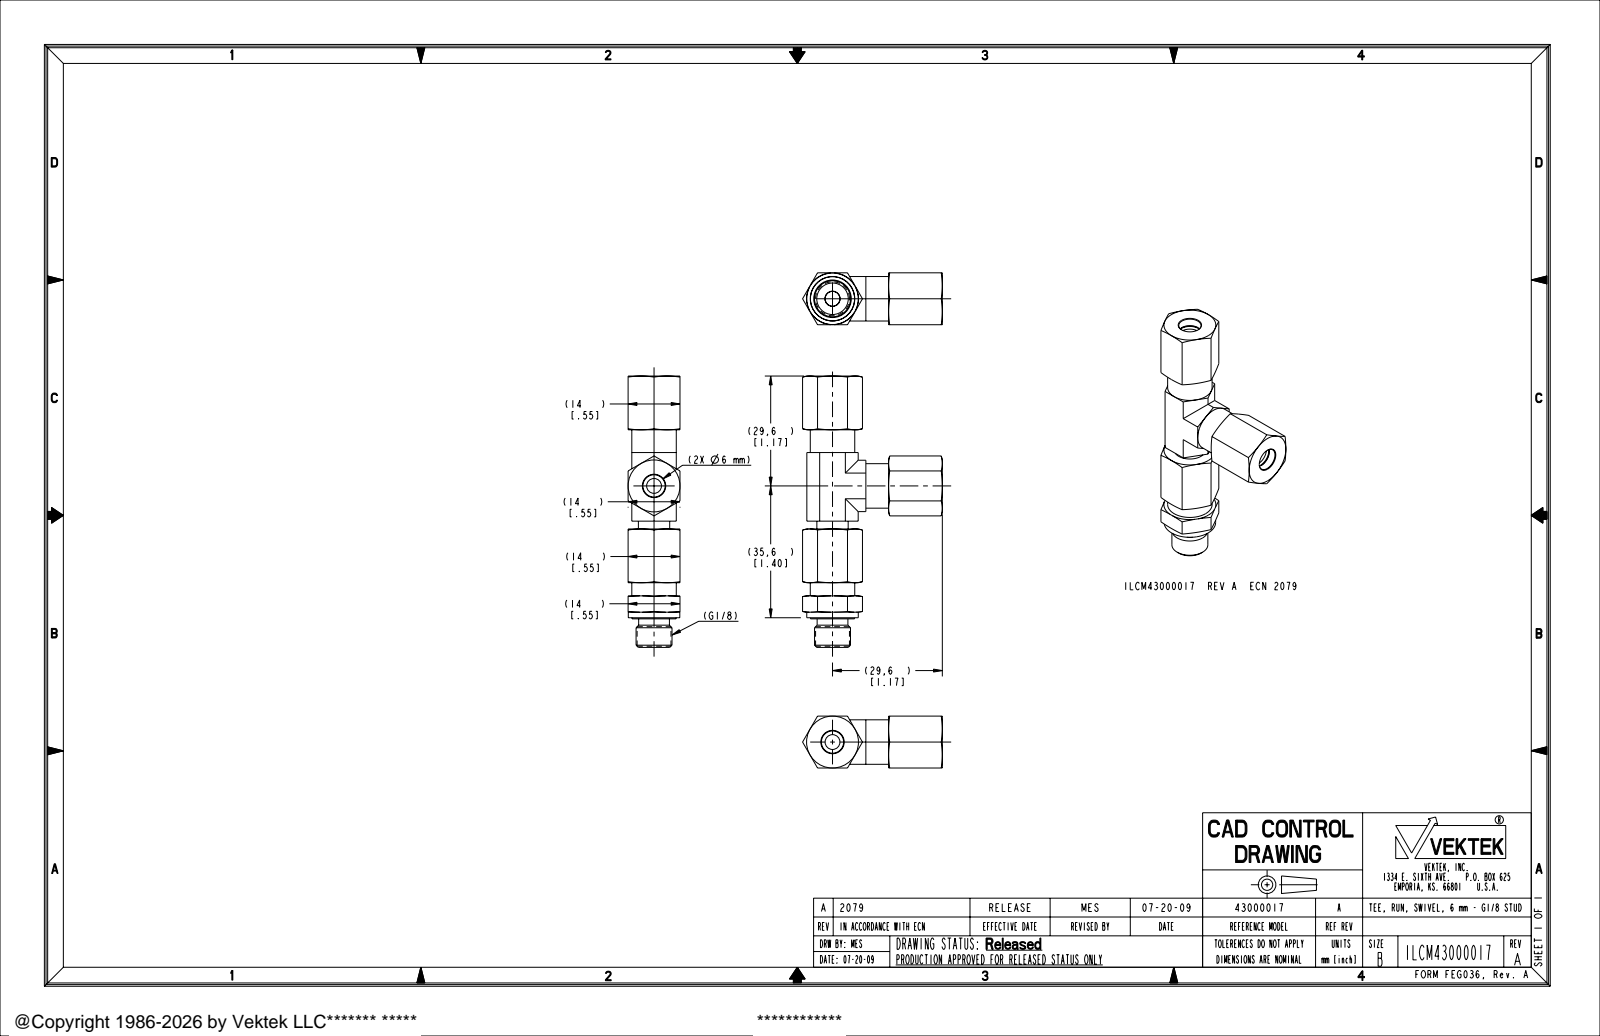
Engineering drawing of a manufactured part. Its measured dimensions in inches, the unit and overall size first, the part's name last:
Units: inches
Overall size (bounding box): 2.881 × 1.485 × 0.551
Round holes (diameter × count): ⌀0.157 ×2, ⌀0.236 ×2, ⌀0.409 ×2, ⌀0.331 ×1, ⌀0.333 ×1
Round bosses / shafts (diameter × count): ⌀0.472 ×2, ⌀0.374 ×2, ⌀0.319 ×2, ⌀0.547 ×1, ⌀0.469 ×1, ⌀0.382 ×1, ⌀0.36 ×1, ⌀0.333 ×1
Main face-to-face distances: 0.551, 0.039, 0.512, 0.472, 1.624, 0.571, 0.083, 1.541, 0.152, 0.419
Volume: 0.68 in³ · Surface area: 13.02 in²
Bodies: 1 solid, 244 faces (78 planar, 60 cylindrical, 106 other)
Part name (STEP PRODUCT): ILCM43000017
STEP written by: PRO/ENGINEER BY PARAMETRIC TECHNOLOGY CORPORATION, 2007460 (AUTOMOTIVE_DESIGN_CC2)
